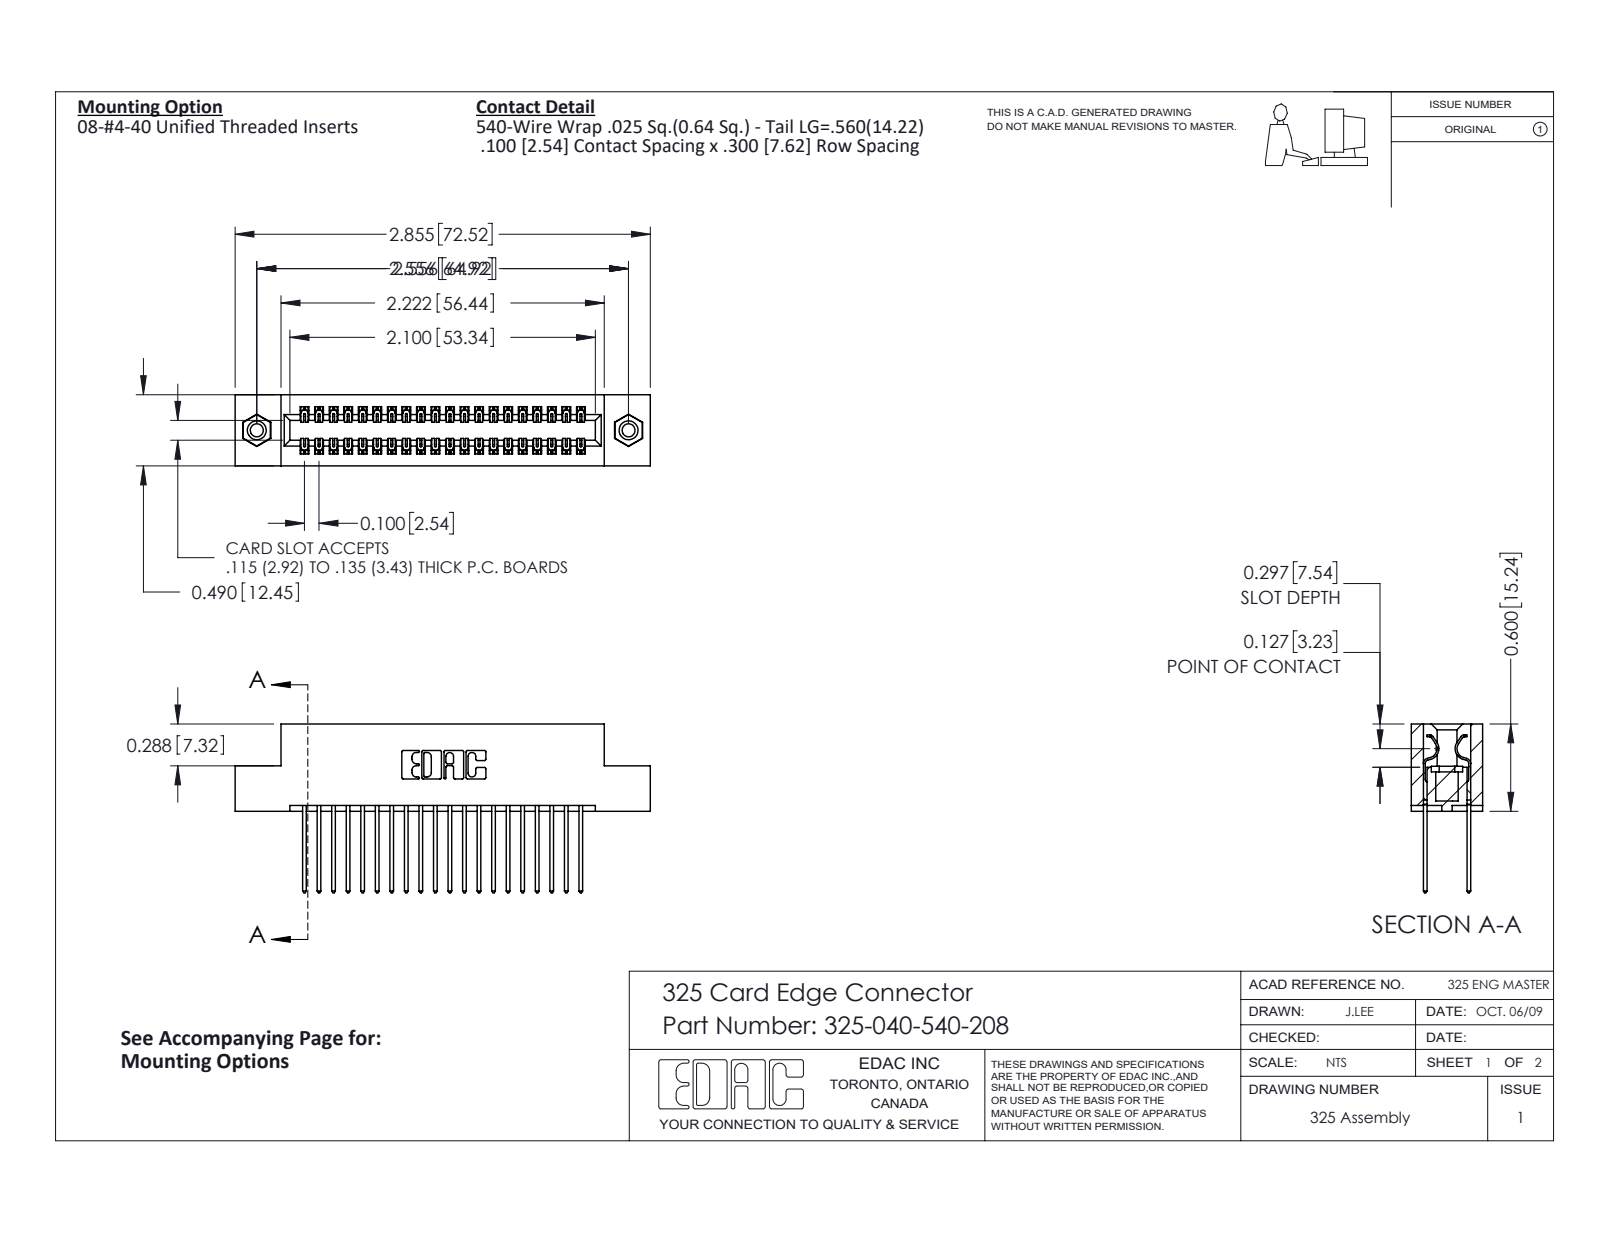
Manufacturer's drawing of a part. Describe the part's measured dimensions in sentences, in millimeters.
The part is named "325 Part_TI; 325-040-540-208; 325-292-001_325-293-140; 345-250-001_345-250-003-102". Its 3-D file was written by "SolidWorks 2016 (CONFIG_CONTROL_DESIGN)". It is 43 solids with 2254 faces: 1542 planar, 696 cylindrical and 16 other. Overall it measures 72.5 by 29.5 by 12.4 millimeters. Its volume is 9 310 cubic millimeters and its surface area 11 480 square millimeters. Round holes: 2 of diameter 2.3, 2 of diameter 3.2, 2 of diameter 4.1. Round bosses or shafts: 2 of diameter 3.9. Partial cylindrical surfaces (rounded edges, fillets, slot ends): 60 of radius 0.2, 40 of radius 0.3, 22 of radius 0.3, 6 of radius 0.2, 6 of radius 0.8, 3 of radius 0.7, 2 of radius 0.4, 2 of radius 0.6. The main face-to-face distances are 2.1, 10.3, 7.6, 2.7, 9.7, 0.6, 12.4, 8.3, 1, 7. The hole center spacings are 64.9.
